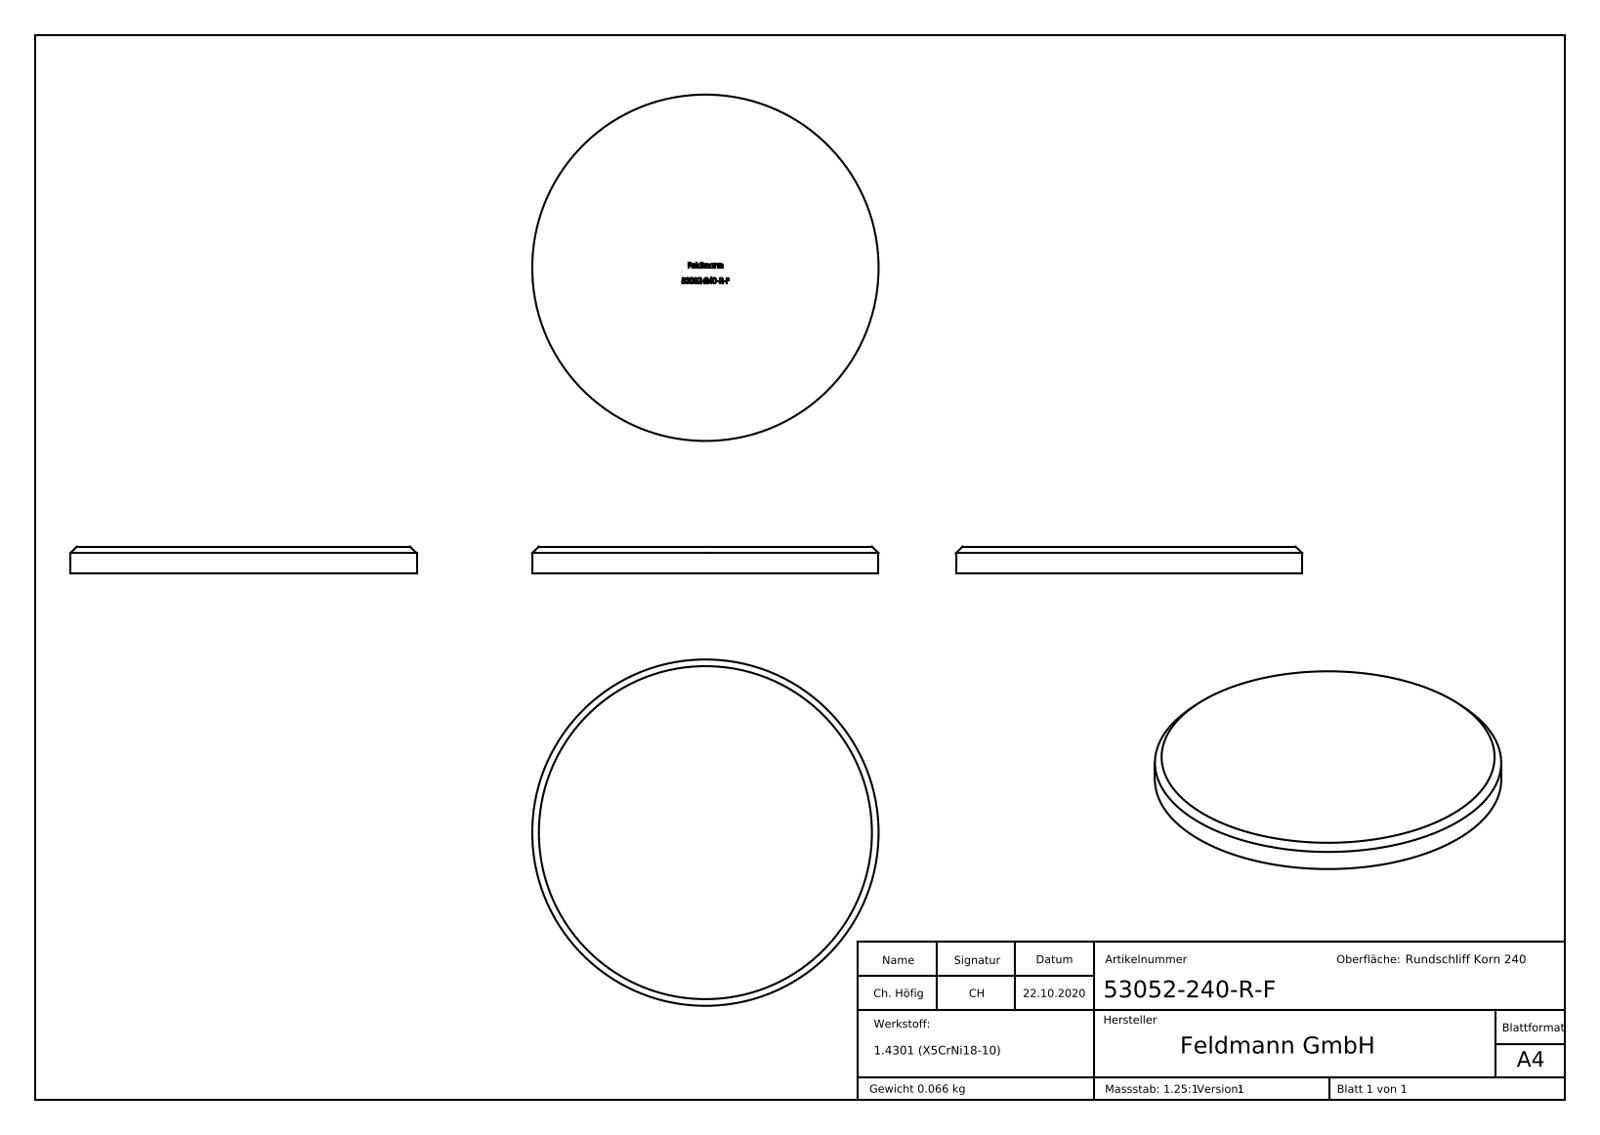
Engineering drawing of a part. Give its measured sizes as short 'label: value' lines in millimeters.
name: 53052-240-R-F
written by: SolidWorks 2018 (CONFIG_CONTROL_DESIGN)
unit: mm
bodies: 1 solid, 274 faces (157 planar, 2 cylindrical, 115 other)
size: 52 × 52 × 4
volume: 8 414 mm³; area: 4 811 mm²
bosses: 1× ⌀52
face distances: 4, 3.9, 2.32, 0.71, 1.21, 0.79, 2.24, 3.49, 1.78, 0.45
